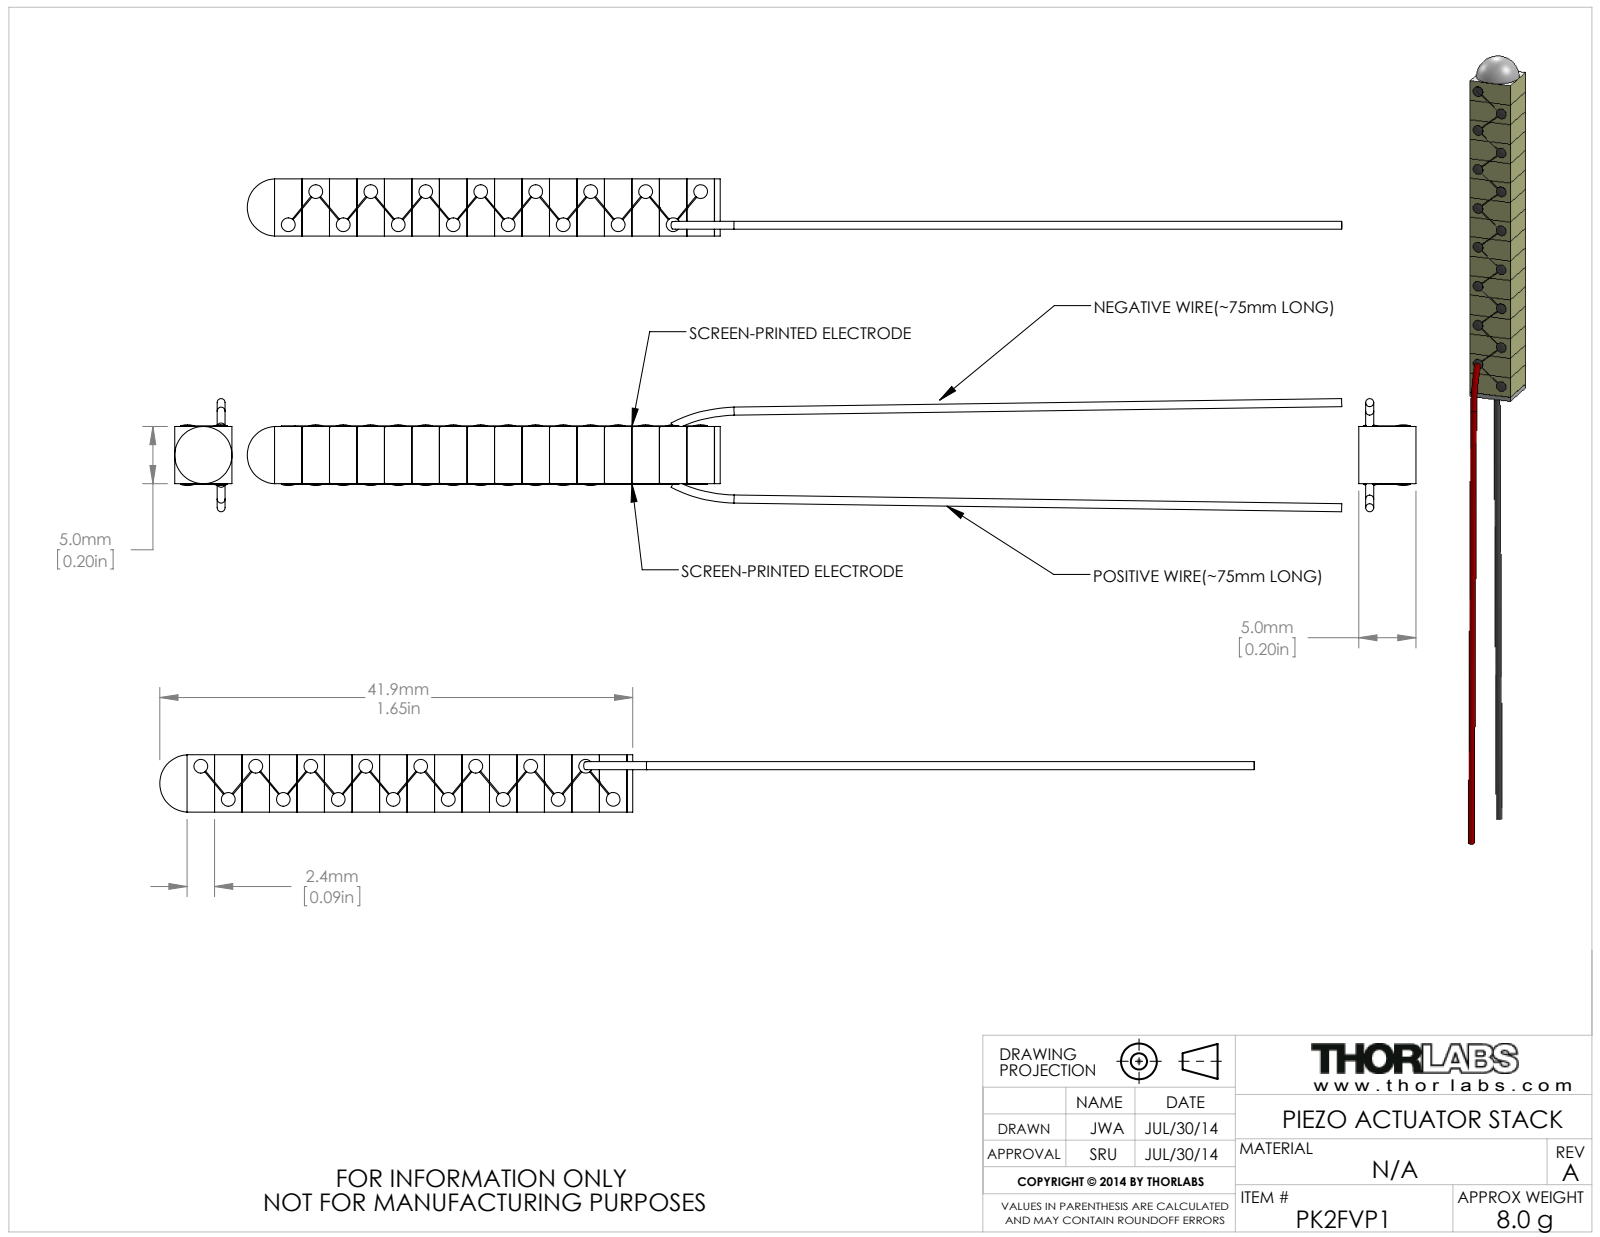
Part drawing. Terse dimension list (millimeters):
name: PK2FVP1
written by: SolidWorks 2012 (AUTOMOTIVE_DESIGN)
unit: mm
bodies: 26 solids, 342 faces (143 planar, 138 cylindrical, 61 other)
size: 95.57 × 9.87 × 5
volume: 1 052 mm³; area: 1 964 mm²
bosses: 16× ⌀1.2, 2× ⌀0.7
face distances: 2.4, 4.8, 7.2, 9.6, 12, 14.4, 16.8, 19.2, 5, 21.6
